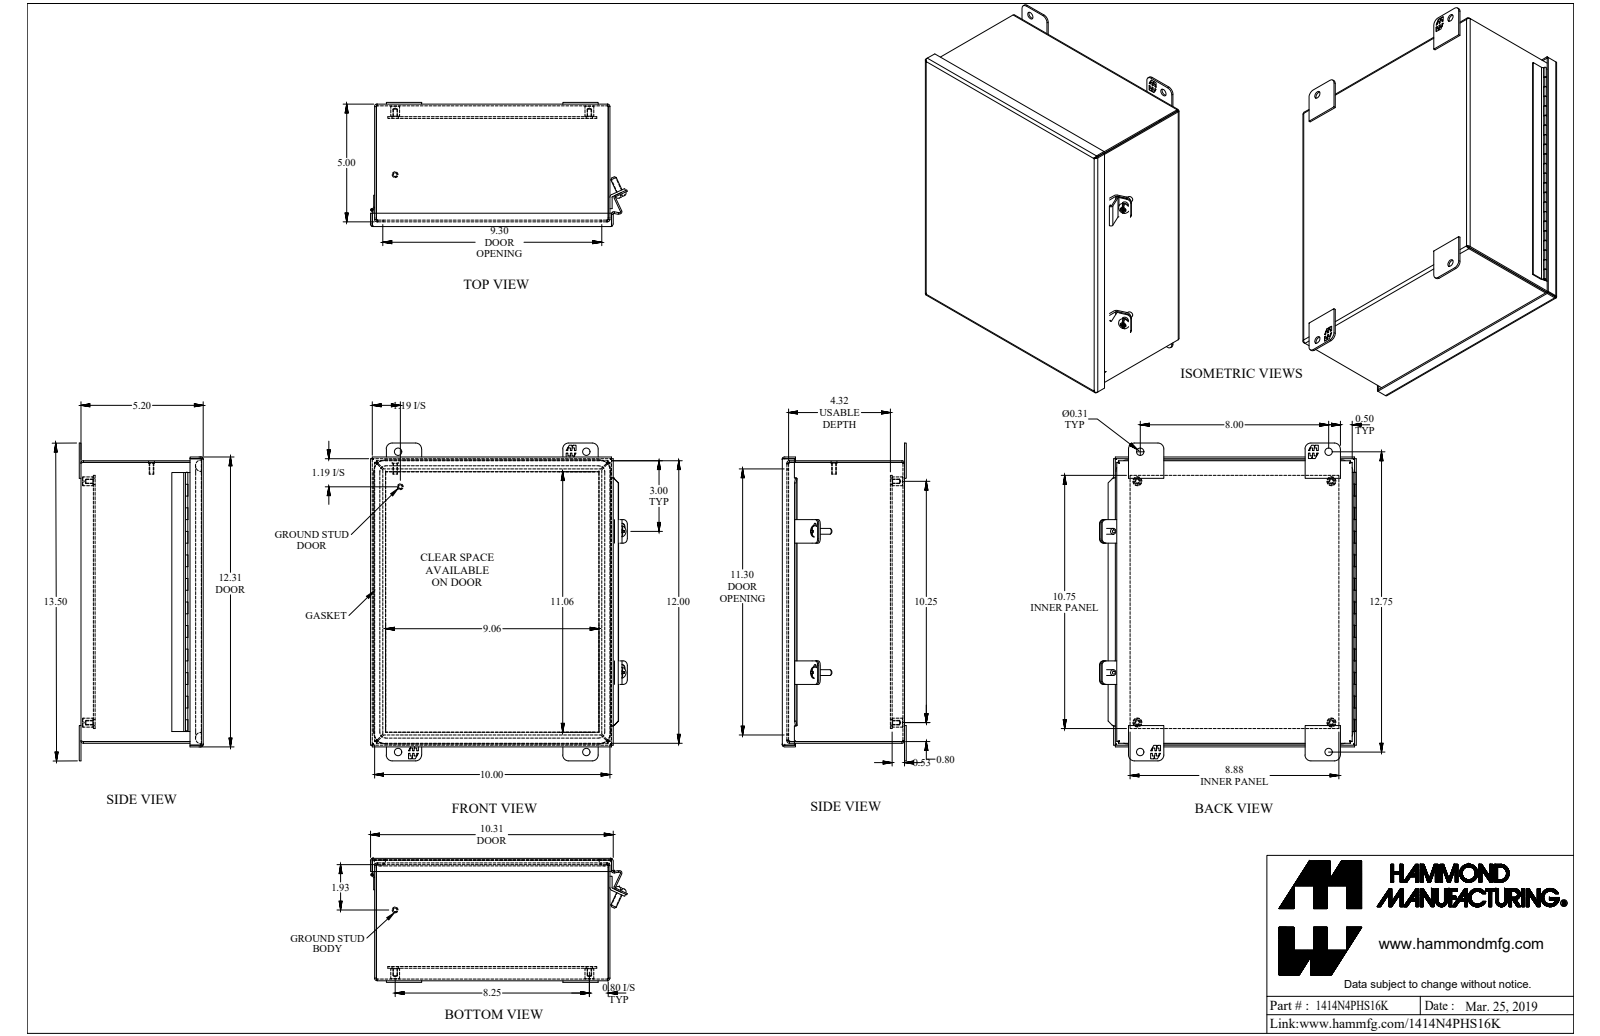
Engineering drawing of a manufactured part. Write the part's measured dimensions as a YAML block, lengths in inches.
part_name: "1414N4PHS16K"
step_written_by: "SolidWorks 2018 (AUTOMOTIVE_DESIGN)"
units: inches
bodies: {solids: 21, faces: 705, planar: 459, cylindrical: 188, other: 58}
overall_size: [13.5, 10.903, 5.269]
volume: 49.67
surface_area: 1358
round_holes:
  - {diameter: 0.156, count: 4}
  - {diameter: 0.265, count: 4}
  - {diameter: 0.313, count: 4}
  - {diameter: 0.213, count: 2}
  - {diameter: 0.05, count: 1}
round_bosses_or_shafts:
  - {diameter: 0.375, count: 4}
  - {diameter: 0.25, count: 4}
  - {diameter: 0.48, count: 2}
  - {diameter: 0.19, count: 2}
  - {diameter: 0.1, count: 1}
  - {diameter: 0.045, count: 1}
partial_cylinders:
  - {radius: 0.25, count: 24}
  - {radius: 0.036, count: 8}
  - {radius: 0.108, count: 8}
  - {radius: 0.188, count: 8}
  - {radius: 0.079, count: 4}
  - {radius: 0.118, count: 4}
  - {radius: 0.141, count: 4}
  - {radius: 0.499, count: 4}
face_to_face_distances: [0.072, 0.532, 0.081, 5.125, 5.197, 5.116, 4.593, 5.044, 9.928, 0.604]
hole_center_spacings: [14.081, 8.22, 13.158, 1.256, 1.256, 8.25, 8.25, 10.25]
